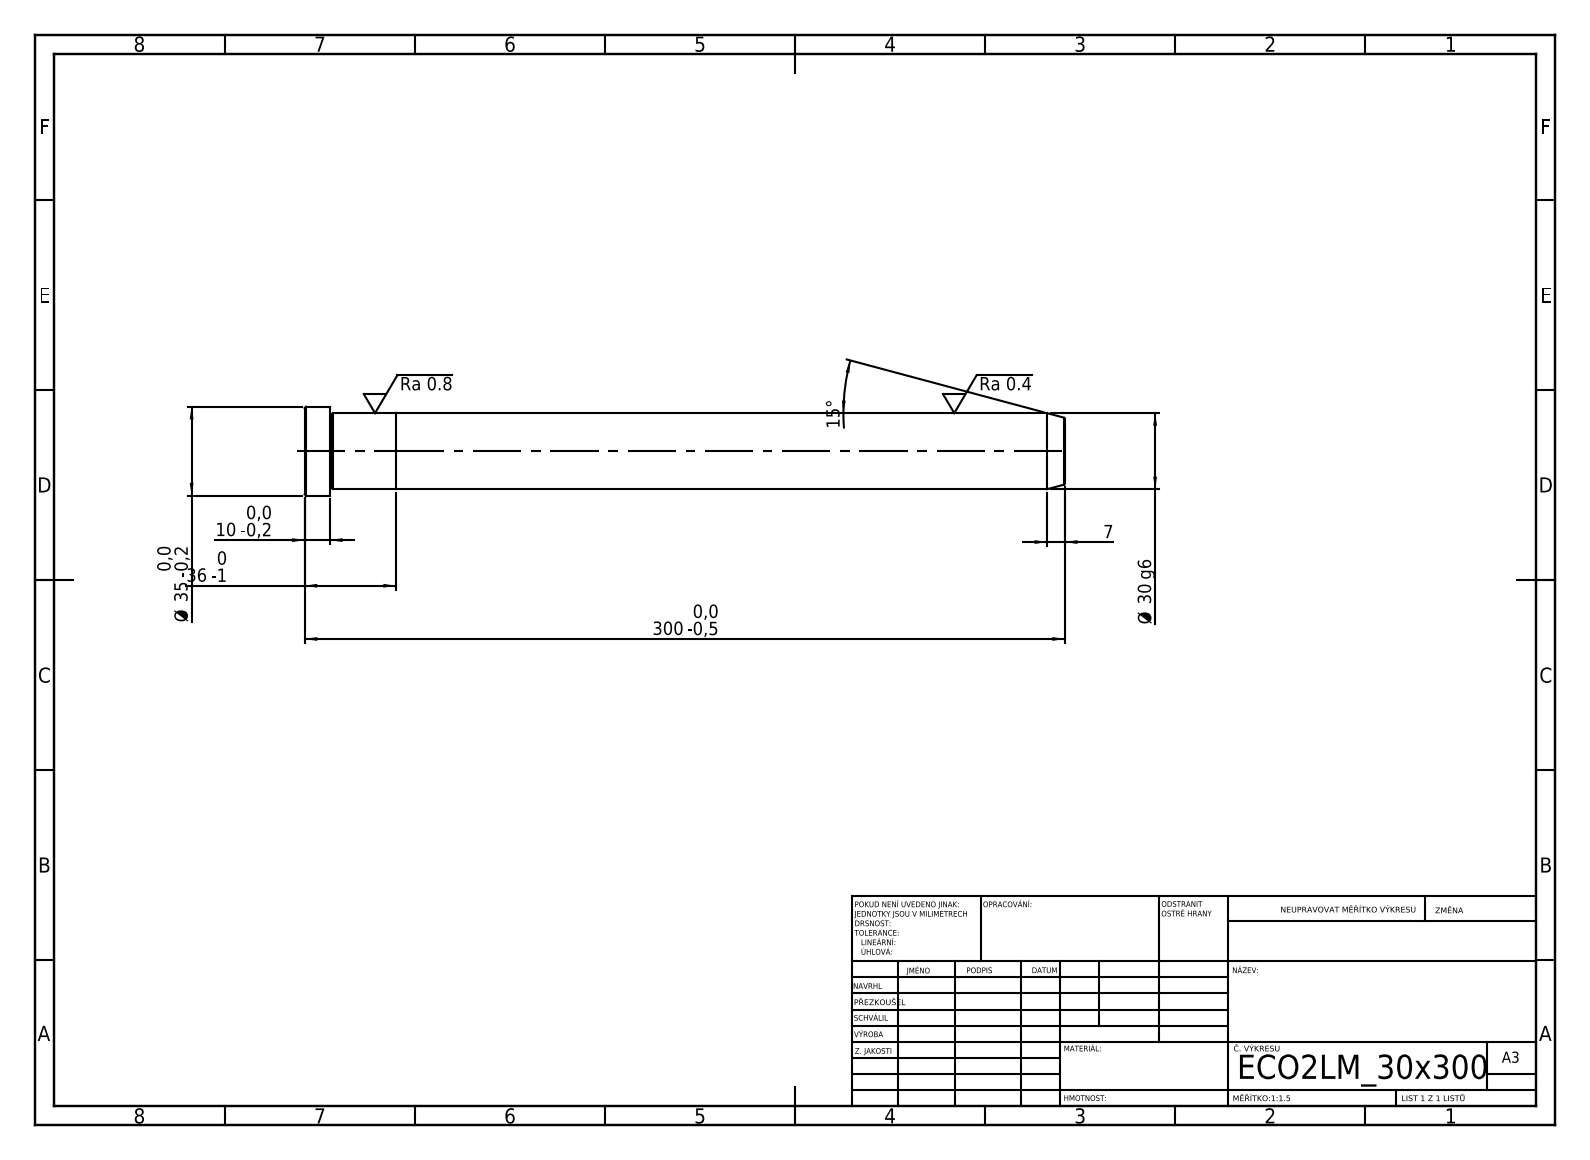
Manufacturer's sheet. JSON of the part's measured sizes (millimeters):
{"step_written_by": "SolidWorks 2019 (CONFIG_CONTROL_DESIGN)", "units": "millimeters", "bodies": {"solids": 2, "faces": 21, "planar": 5, "cylindrical": 6, "other": 10}, "overall_size": [300, 35, 35], "volume_mm3": 213965, "surface_area_mm2": 31593, "round_bosses_or_shafts": [[35, 1], [30, 1]], "face_to_face_distances": [36, 264, 300, 290, 26, 10]}
